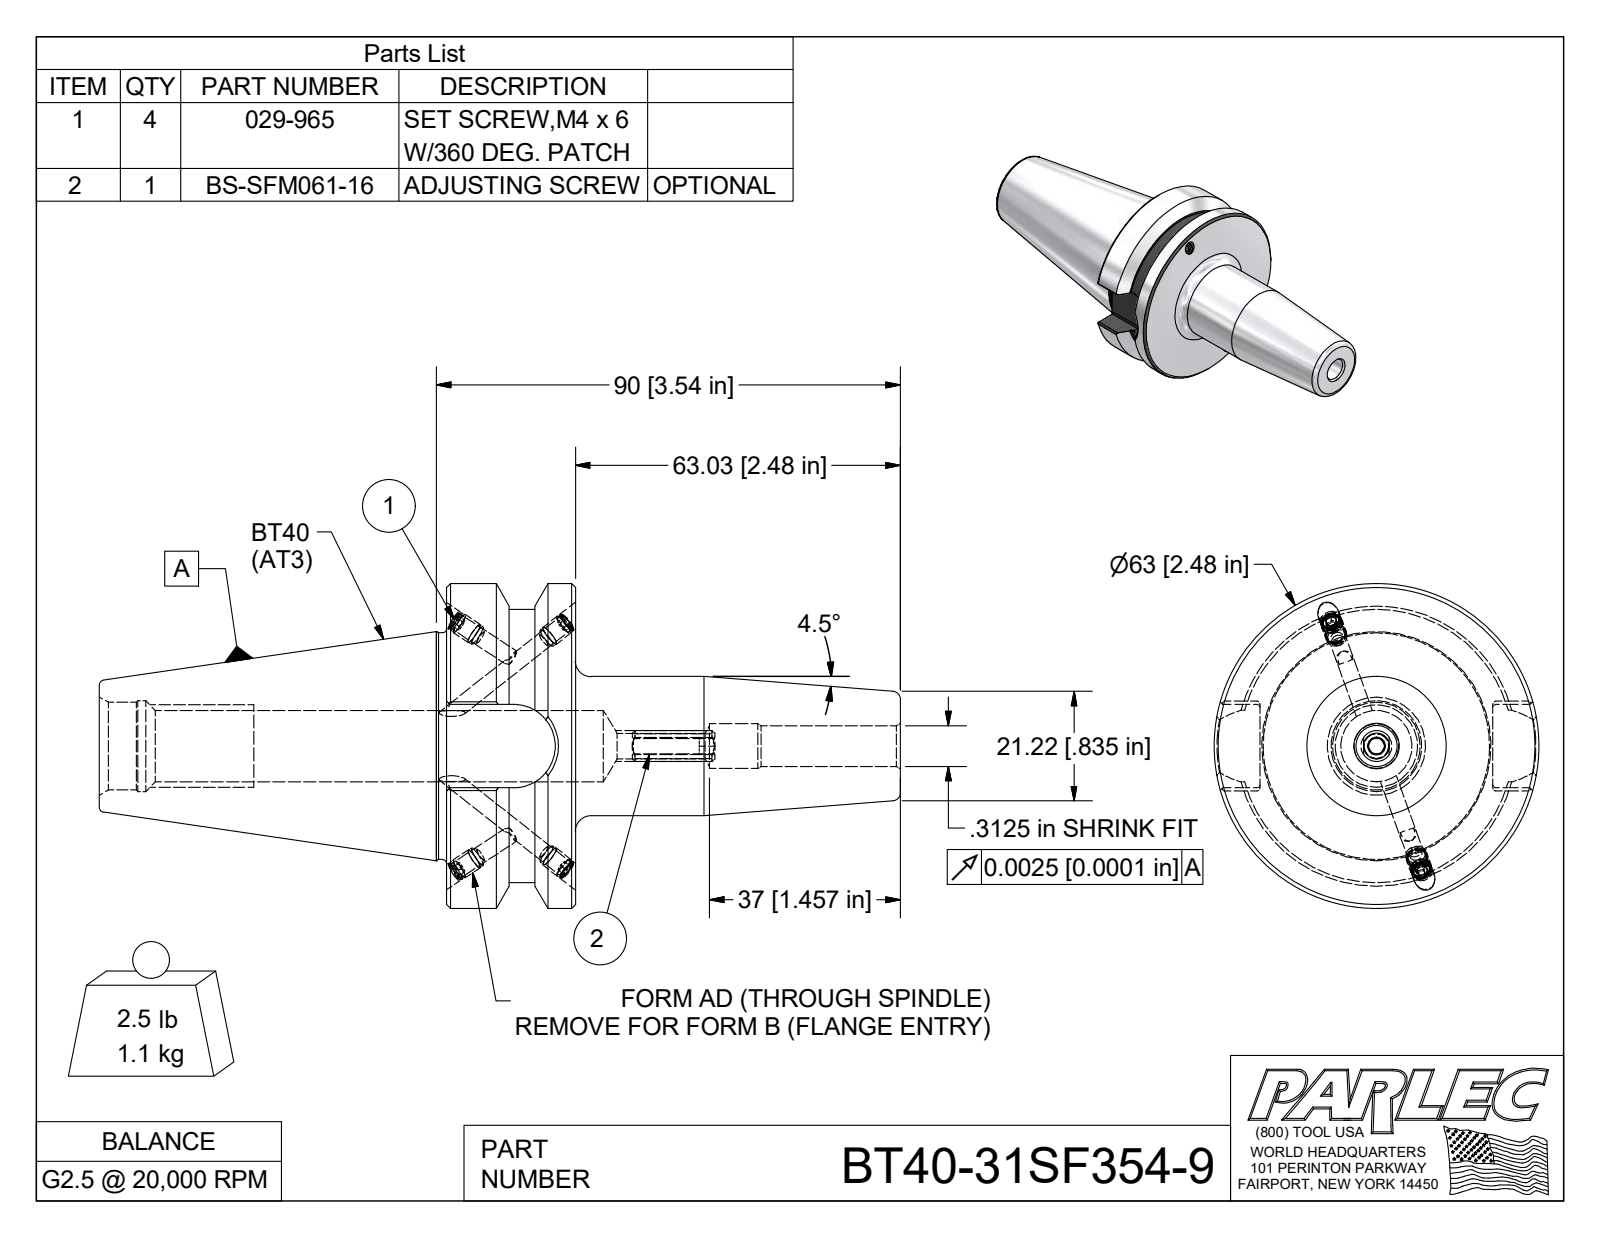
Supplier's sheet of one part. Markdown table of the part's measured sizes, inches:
| quantity | value |
| --- | --- |
| part name | BT40-31SF354-9; BT40BC-31SF354-9-1; 029-965; BS-SFM061-16 |
| STEP written by | Autodesk Inventor 2009 (AUTOMOTIVE_DESIGN) |
| units | inches |
| bodies | 6 solids, 178 faces (79 planar, 43 cylindrical, 56 other) |
| overall size | 6.118 × 2.48 × 2.48 |
| volume | 9.004 in³ |
| surface area | 47.21 in² |
| round holes (diameter × count) | 0.13 × 4, 0.161 × 4, 0.312 × 1, 0.342 × 1, 0.694 × 1 |
| round bosses / shafts (diameter × count) | 0.165 × 4, 0.157 × 4, 2.48 × 1, 2.087 × 1, 1.75 × 1, 1.73 × 1, 1.063 × 1 |
| partial cylindrical surfaces (radius × count) | 0.02 × 8, 0.118 × 1, 0.319 × 1 |
| main face-to-face distances | 0.984, 1.78, 3.465, 2.481, 2.653, 3.637, 6.119, 0.637, 0.197, 0.792 |
